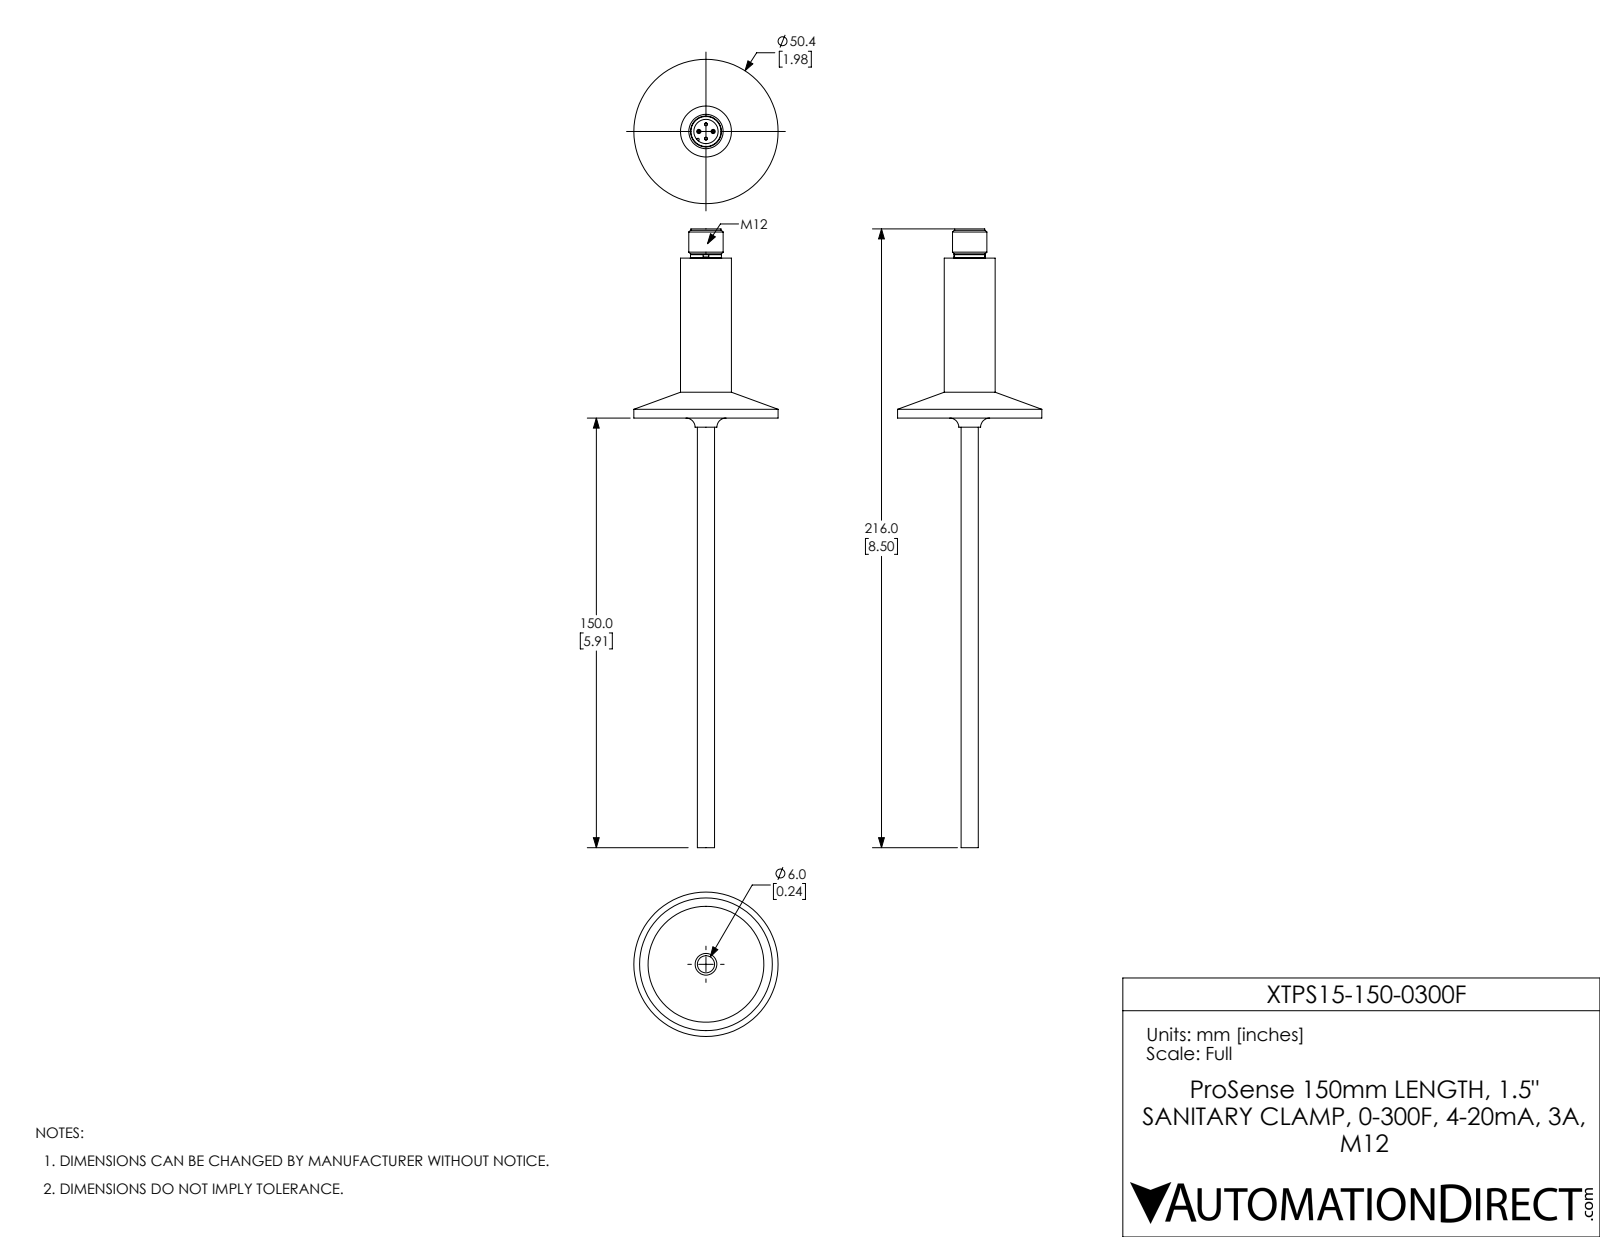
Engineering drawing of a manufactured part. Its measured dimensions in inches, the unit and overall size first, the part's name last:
Units: inches
Overall size (bounding box): 8.505 × 1.984 × 1.984
Round holes (diameter × count): ⌀0.335 ×1
Round bosses / shafts (diameter × count): ⌀0.04 ×4, ⌀1.984 ×1, ⌀0.701 ×1, ⌀0.472 ×1, ⌀0.425 ×1, ⌀0.421 ×1, ⌀0.413 ×1, ⌀0.236 ×1
Partial cylindrical surfaces — rounded edges, fillets, slot ends (radius × count): R0.016 ×1
Main face-to-face distances: 2.198, 2.245, 0.048, 2.599, 0.402, 0.354, 5.906, 8.103, 8.151, 8.505
Volume: 1.715 in³ · Surface area: 16.97 in²
Bodies: 1 solid, 80 faces (25 planar, 25 cylindrical, 30 other)
Part name (STEP PRODUCT): XTPS15-150-0300F
STEP written by: SolidWorks 2017 (AUTOMOTIVE_DESIGN)
